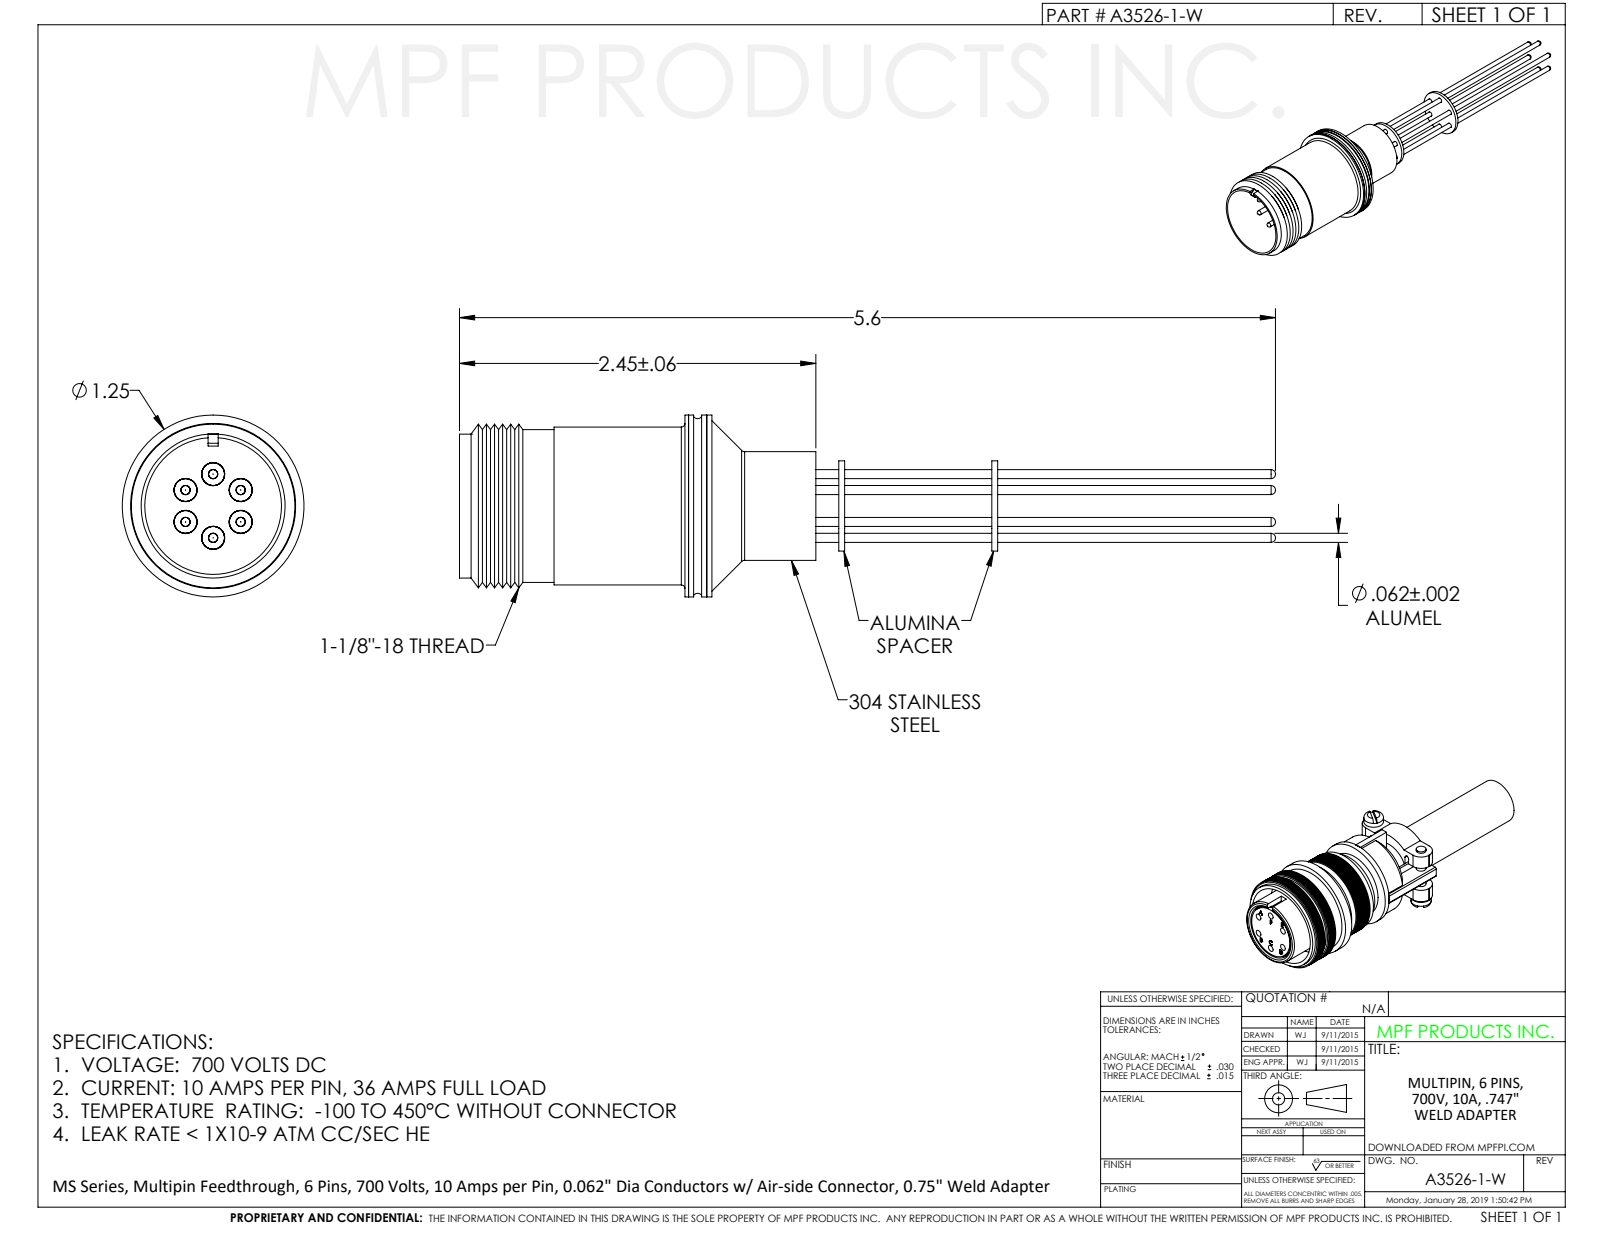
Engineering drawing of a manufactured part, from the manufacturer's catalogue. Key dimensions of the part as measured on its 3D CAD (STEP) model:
Part name (STEP PRODUCT): A3526-1-W
STEP written by: SolidWorks 2012 (CONFIG_CONTROL_DESIGN)
Units: inches
Bodies: 24 solids, 338 faces (85 planar, 154 cylindrical, 99 other)
Overall size (bounding box): 5.645 × 1.25 × 1.25
Volume: 0.741 in³ · Surface area: 37.84 in²
Round holes (diameter × count): ⌀0.059 ×6, ⌀0.06 ×6, ⌀0.064 ×6, ⌀0.141 ×6, ⌀0.157 ×6, ⌀0.159 ×6, ⌀0.675 ×1, ⌀0.94 ×1, ⌀0.96 ×1, ⌀0.97 ×1, ⌀1.035 ×1
Round bosses / shafts (diameter × count): ⌀0.187 ×6, ⌀0.157 ×6, ⌀0.062 ×6, ⌀1.25 ×1, ⌀1.085 ×1, ⌀1.05 ×1, ⌀1.02 ×1, ⌀1 ×1
Main face-to-face distances: 0.125, 0.43, 0.555, 0.05, 0.38, 0.505, 0.04, 2.22, 2.27, 2.311
Hole centre spacings: 0.219, 0.379, 0.38, 0.438, 0.438
